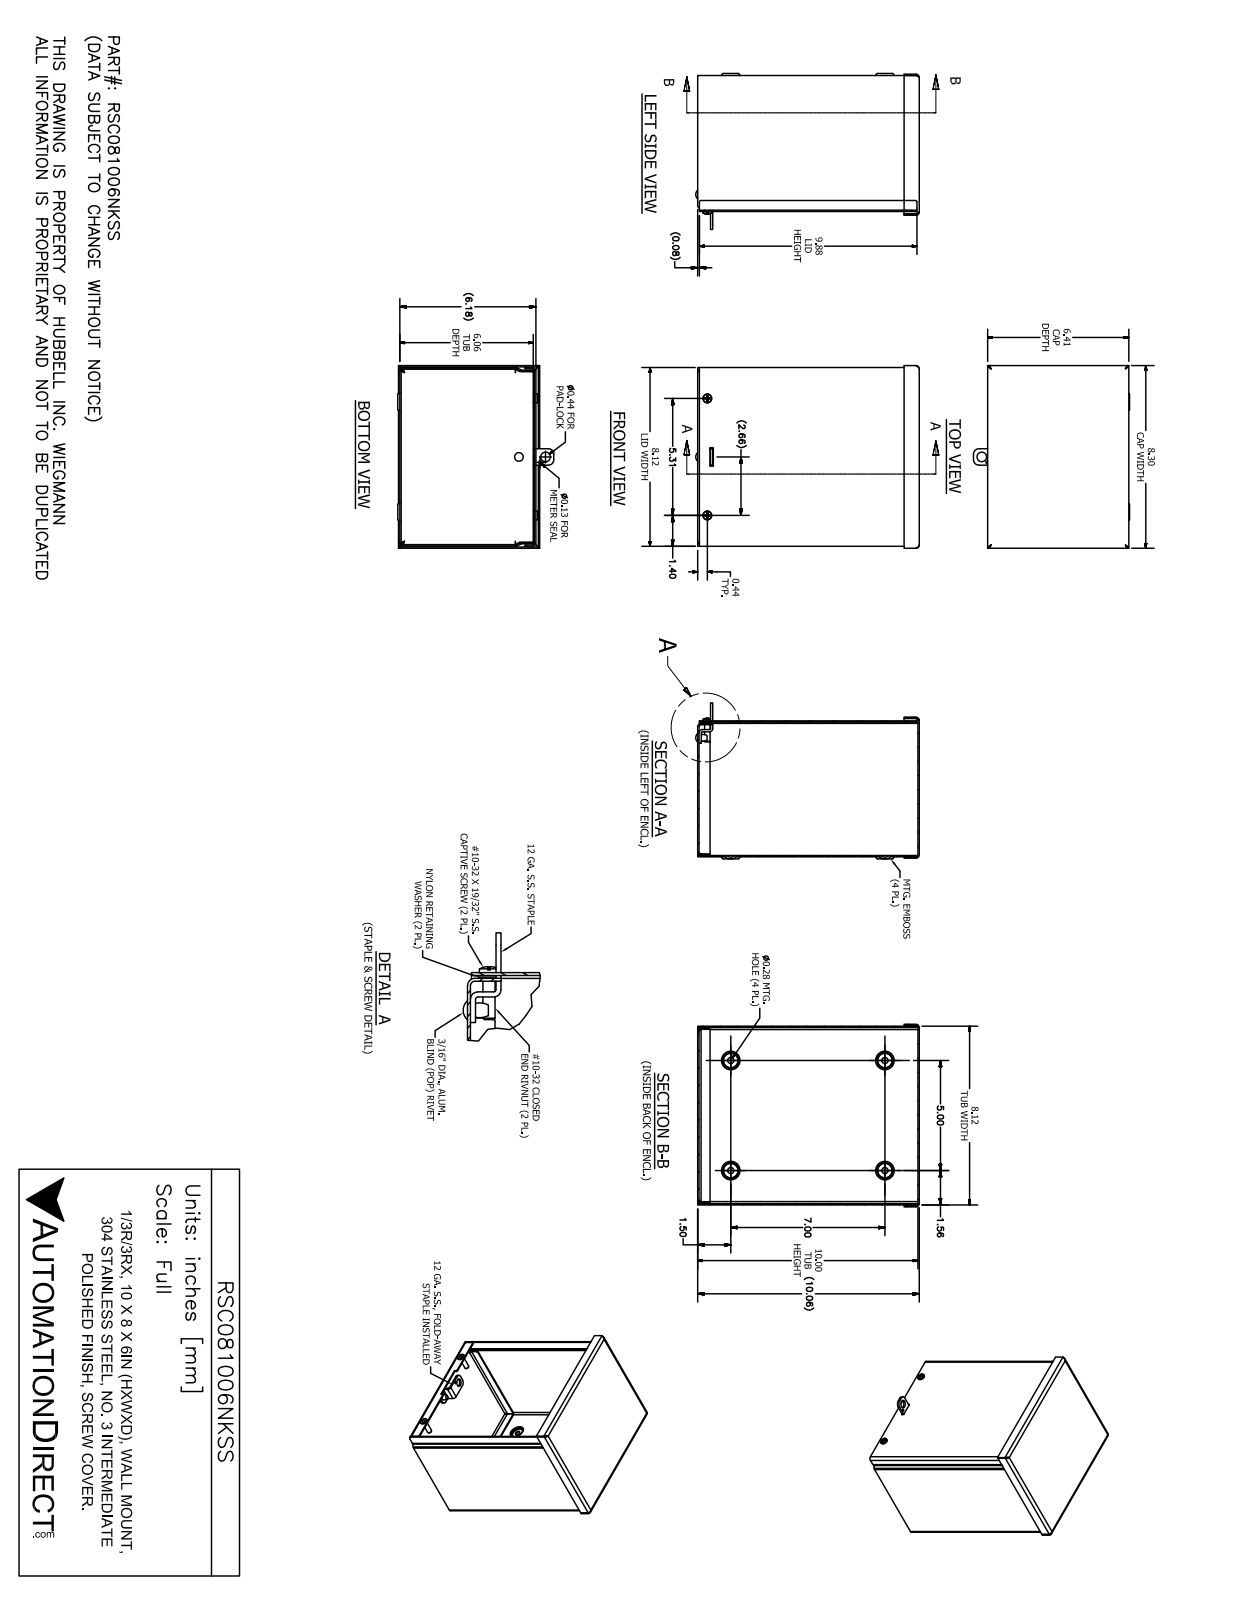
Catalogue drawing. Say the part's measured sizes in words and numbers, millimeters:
The part is named "RSC081006NKSS". Its 3-D file was written by "SolidWorks 2017 (AUTOMOTIVE_DESIGN)". It is 12 solids with 369 faces: 191 planar, 93 cylindrical and 85 other. Overall it measures 257.8 by 210.8 by 179.9 millimeters. Its volume is 409 000 cubic millimeters and its surface area 552 000 square millimeters. Round holes: 4 of diameter 6.4, 4 of diameter 7.1, 2 of diameter 4, 2 of diameter 5, 2 of diameter 6.5, 2 of diameter 7.1, 1 of diameter 3.2, 1 of diameter 5, 1 of diameter 5.1, 1 of diameter 11.1. Round bosses or shafts: 2 of diameter 11.5, 2 of diameter 10.3, 2 of diameter 6.3, 2 of diameter 4.2, 1 of diameter 4.7. Partial cylindrical surfaces (rounded edges, fillets, slot ends): 16 of radius 2.4, 16 of radius 3.9, 6 of radius 0.8, 4 of radius 6.4, 2 of radius 1.2, 2 of radius 1.3, 2 of radius 1.6, 2 of radius 2.3. The main face-to-face distances are 1.5, 155.4, 204.7, 254, 156.9, 153.9, 203.2, 206.2, 255.5, 252.5. The hole center spacings are 27.3, 28.1, 127, 133.7, 133.9, 135, 177.8, 204.8.
